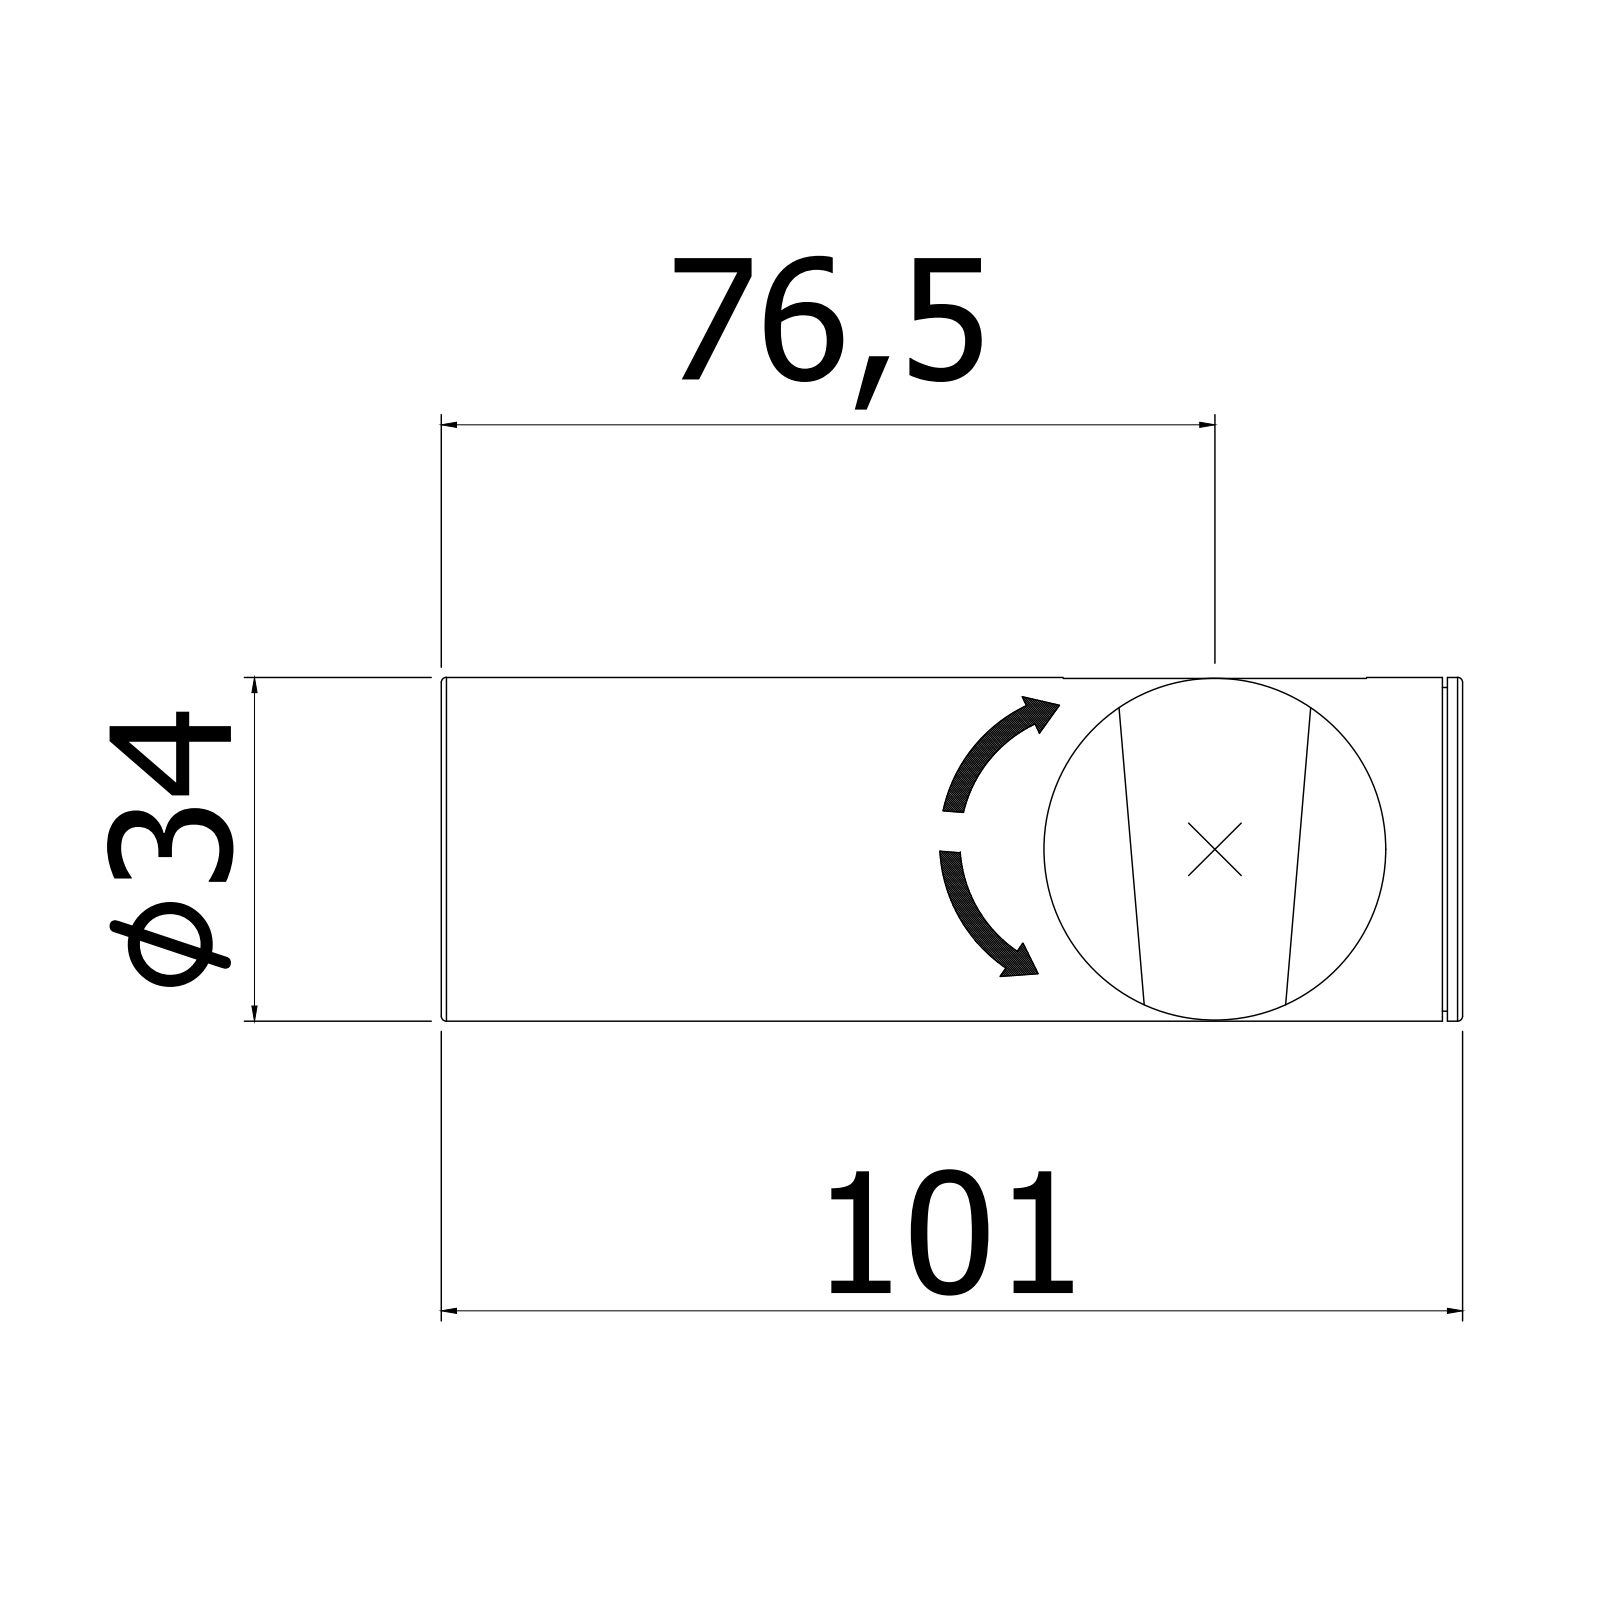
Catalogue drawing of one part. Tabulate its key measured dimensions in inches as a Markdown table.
| quantity | value |
| --- | --- |
| part name | ZSUP022CR |
| STEP written by | CREO PARAMETRIC BY PTC INC, 2020044 (CONFIG_CONTROL_DESIGN) |
| units | inches |
| bodies | 2 solids, 223 faces (112 planar, 88 cylindrical, 23 other) |
| overall size | 3.976 × 2.778 × 1.358 |
| volume | 2.876 in³ |
| surface area | 61 in² |
| round holes (diameter × count) | 0.138 × 1, 0.307 × 1, 0.622 × 1, 0.63 × 1, 0.807 × 1, 0.846 × 1, 1.094 × 1, 1.142 × 1, 1.161 × 1, 1.201 × 1, 1.232 × 1 |
| round bosses / shafts (diameter × count) | 1.358 × 1, 1.339 × 1, 1.331 × 1, 1.319 × 1, 1.22 × 1, 1.181 × 1, 0.839 × 1, 0.78 × 1 |
| partial cylindrical surfaces (radius × count) | 0.012 × 6, 0.079 × 4, 0.197 × 4, 0.205 × 4, 0.144 × 1, 0.222 × 1, 0.23 × 1, 0.433 × 1 |
| main face-to-face distances | 0.079, 3.976, 0.098, 3.898, 3.799, 3.878, 0.413, 0.335, 0.039, 0.453 |
